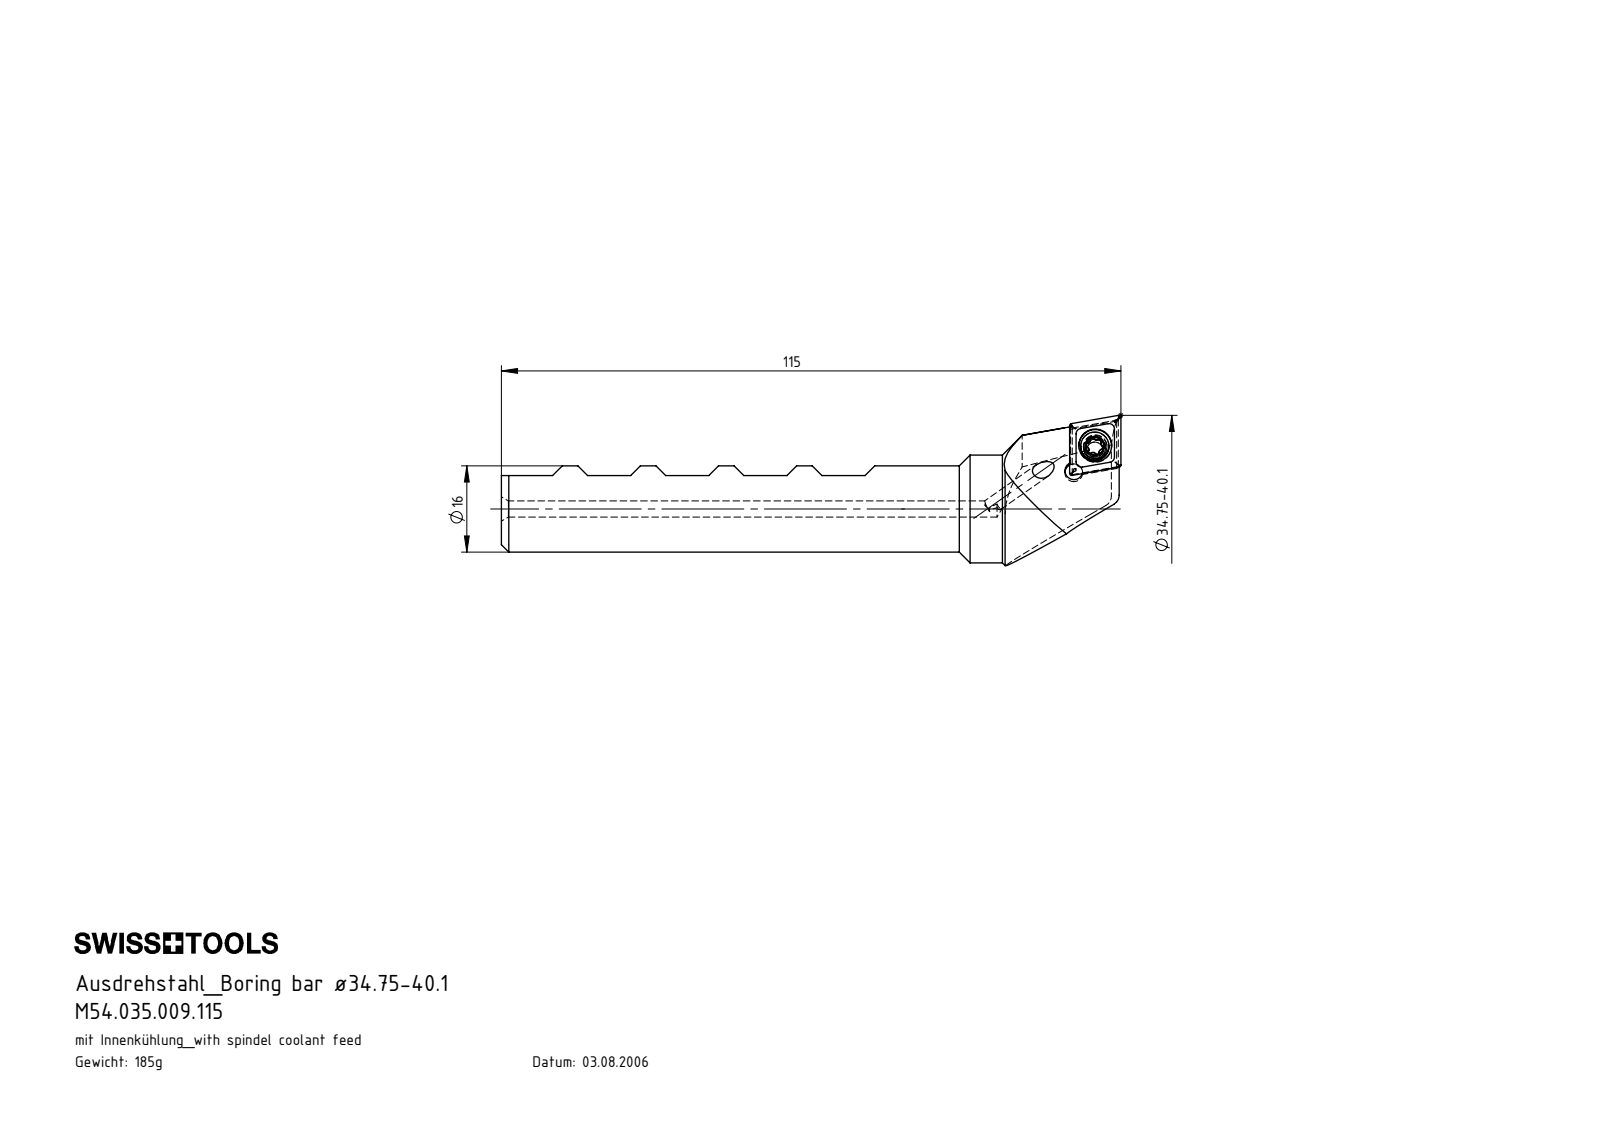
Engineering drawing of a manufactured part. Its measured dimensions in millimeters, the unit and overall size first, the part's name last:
Units: millimetres
Overall size (bounding box): 115 × 27.88 × 22.08
Round holes (diameter × count): ⌀3 ×2, ⌀3.3 ×2, ⌀4.4 ×1, ⌀6.1 ×1
Round bosses / shafts (diameter × count): ⌀20 ×1, ⌀16 ×1, ⌀5.25 ×1, ⌀4 ×1
Partial cylindrical surfaces — rounded edges, fillets, slot ends (radius × count): R0.34 ×6, R0.59 ×6, R2 ×1, R10.5 ×1, R12 ×1
Main face-to-face distances: 8.04, 10.25, 20.5, 30.76, 20.51, 11.81, 3.77, 12.01, 3.97, 30.75
Hole centre spacings: 6.07, 6.2
Volume: 23 609 mm³ · Surface area: 8 114 mm²
Bodies: 3 solids, 114 faces (45 planar, 25 cylindrical, 44 other)
Part name (STEP PRODUCT): B35.WCB.K11.115; WCB-ER2.001.009_A; CCMT09T304; B35-WCB.K11.115_B
STEP written by: SolidWorks 2017 (AUTOMOTIVE_DESIGN)
